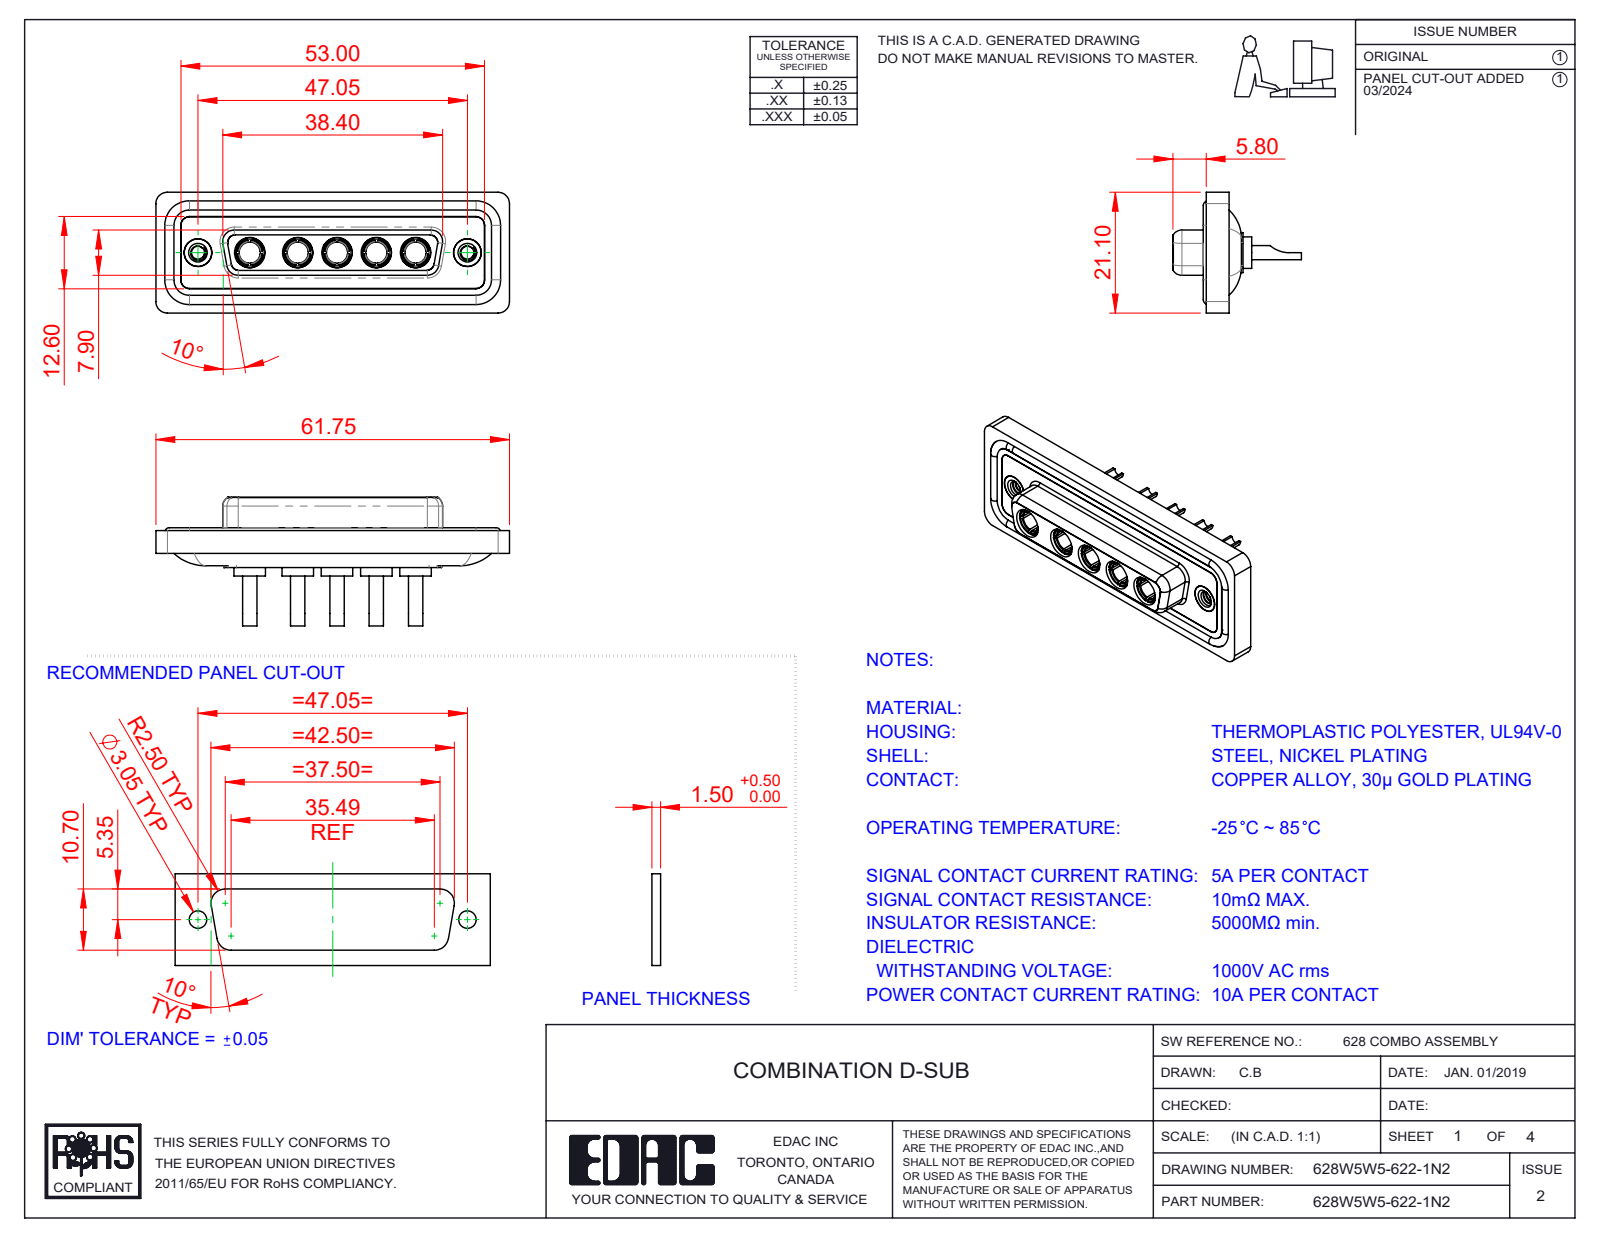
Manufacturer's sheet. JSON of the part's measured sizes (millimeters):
{"part_name": "628Combo Shell Front_25 Contacts; 628Combo Waterproof Housing_25 Contacts; 628Combo Threaded Rivet_2; Power Socket_10A SC (+3 more)", "step_written_by": "SolidWorks 2023 (CONFIG_CONTROL_DESIGN)", "units": "millimeters", "bodies": {"solids": 17, "faces": 781, "planar": 260, "cylindrical": 318, "other": 203}, "overall_size": [61.75, 22.45, 21.1], "volume_mm3": 8159, "surface_area_mm2": 13654, "round_holes": [[4.85, 7], [1.7, 5], [3.7, 5], [5.3, 5], [2.26, 2], [4, 2], [4.05, 2], [5, 2]], "round_bosses_or_shafts": [[5.5, 5], [5.2, 5], [4.96, 5], [4.75, 5], [3.75, 5], [2.5, 5], [1.6, 4], [4.95, 2]], "partial_cylinders_radius": [[1.5, 22], [2, 18], [1.35, 8], [1.6, 8], [2.1, 5], [0.25, 4], [0.5, 4], [0.6, 4]], "face_to_face_distances": [0.4, 1.8, 7.45, 5.65, 0.5, 7.05, 6.6, 1.6, 1.1, 2.9], "hole_center_spacings": [6.86, 9.04, 13.72, 38.01, 8.39, 15.25, 15.9, 17.43]}
